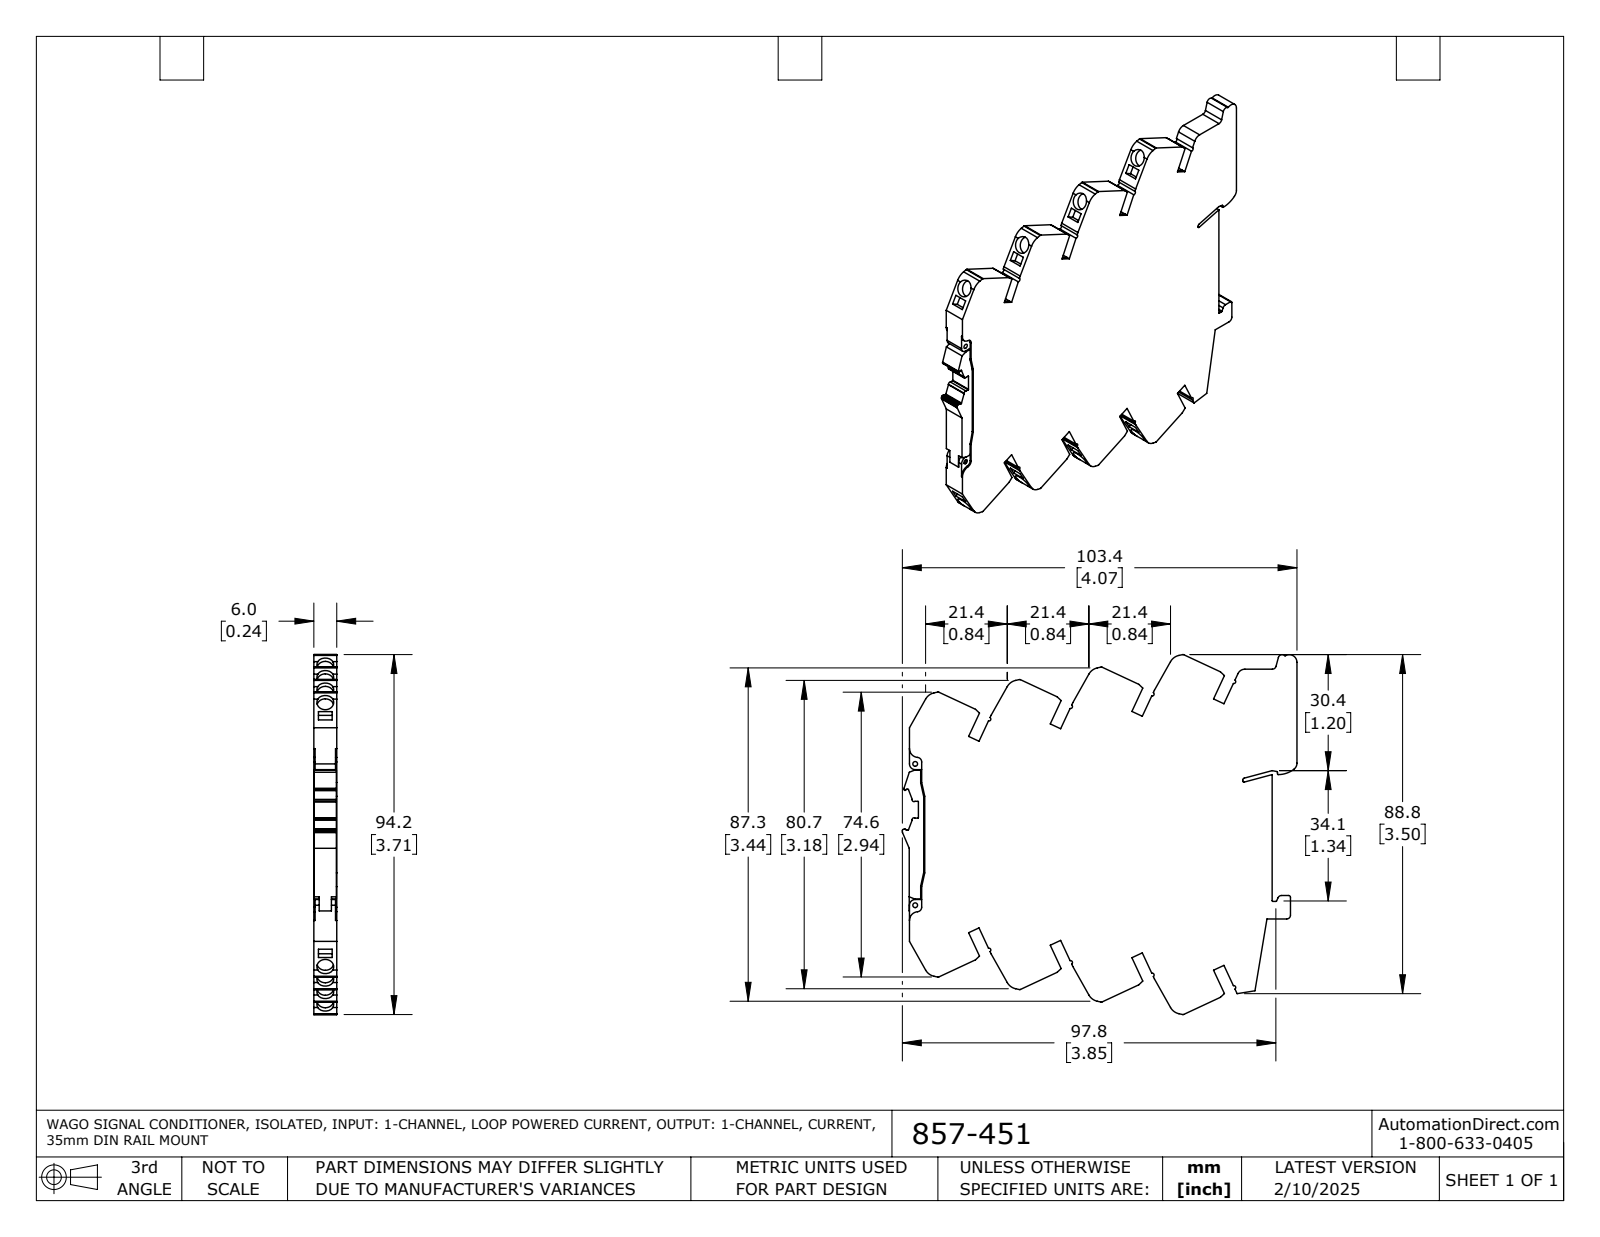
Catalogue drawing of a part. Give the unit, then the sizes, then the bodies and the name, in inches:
Units: inches
Overall size (bounding box): 4.069 × 3.711 × 0.236
Round holes (diameter × count): ⌀0.173 ×8, ⌀0.049 ×2
Partial cylindrical surfaces — rounded edges, fillets, slot ends (radius × count): R0.02 ×12, R0.008 ×11, R0.016 ×8, R0.132 ×8, R0.039 ×4, R0.012 ×3, R0.079 ×3, R0.018 ×2
Main face-to-face distances: 0.236, 0.708, 0.67, 0.473, 0.232, 0.472, 0.118, 0.945, 1.417, 0.256
Hole centre spacings: 0.526, 0.525, 1.051, 1.051, 1.052, 1.457, 1.576, 1.577
Volume: 2.681 in³ · Surface area: 29.86 in²
Bodies: 1 solid, 317 faces (219 planar, 98 cylindrical, 0 other)
Part name (STEP PRODUCT): 857-451
STEP written by: SolidWorks 2021 (AUTOMOTIVE_DESIGN)
